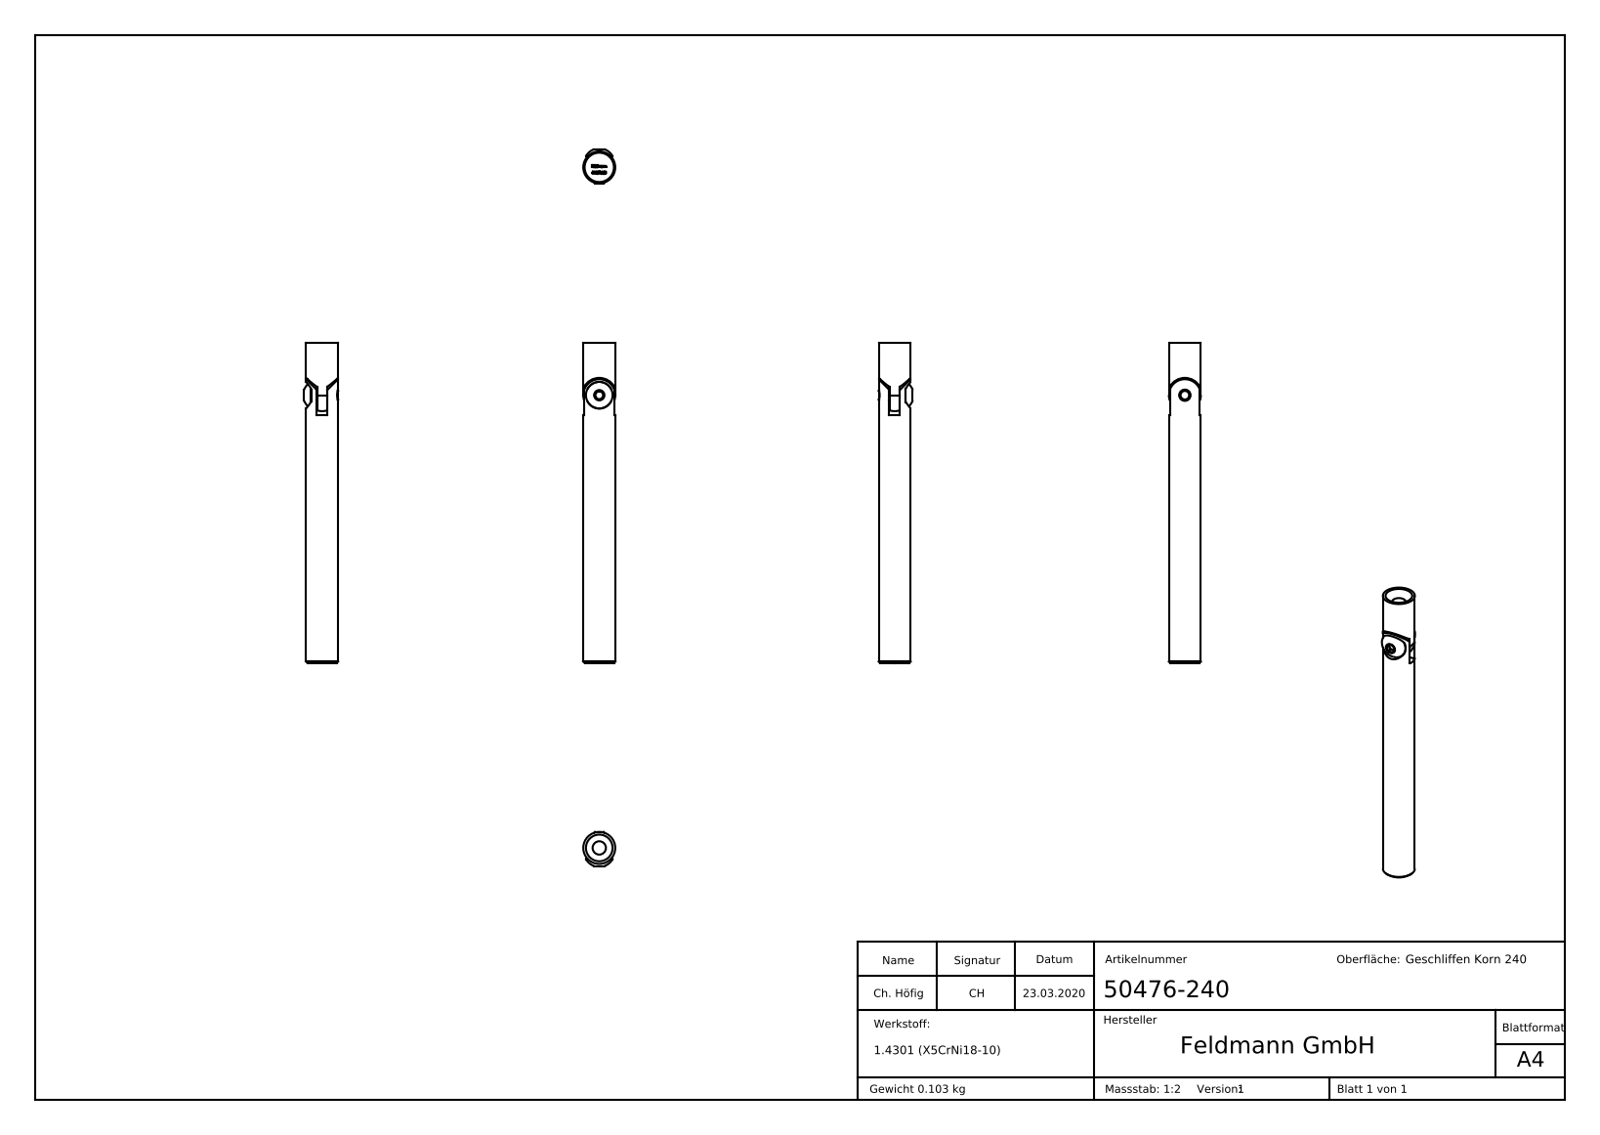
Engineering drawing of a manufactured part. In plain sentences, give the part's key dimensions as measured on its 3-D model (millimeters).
The part is named "50476-240 Teil2_50476-240 Teil4; ISO 7380 M5x10; 50476-240; 50476-240 Teil1_50476-240 Teil3 (+3 more)". Its 3-D file was written by "SolidWorks 2015 (CONFIG_CONTROL_DESIGN)". It is 3 solids with 264 faces: 148 planar, 14 cylindrical and 102 other. Overall it measures 120 by 14.8 by 12 millimeters. Its volume is 13 024 cubic millimeters and its surface area 5 982 square millimeters. Round holes: 1 of diameter 4.2, 1 of diameter 5, 1 of diameter 5.5, 1 of diameter 10. Round bosses or shafts: 1 of diameter 12, 1 of diameter 4.02. Partial cylindrical surfaces (rounded edges, fillets, slot ends): 1 of radius 6, 1 of radius 6.5. The main face-to-face distances are 3.88, 4, 6, 2, 5.88, 3.76, 2.12, 93, 120, 27.
